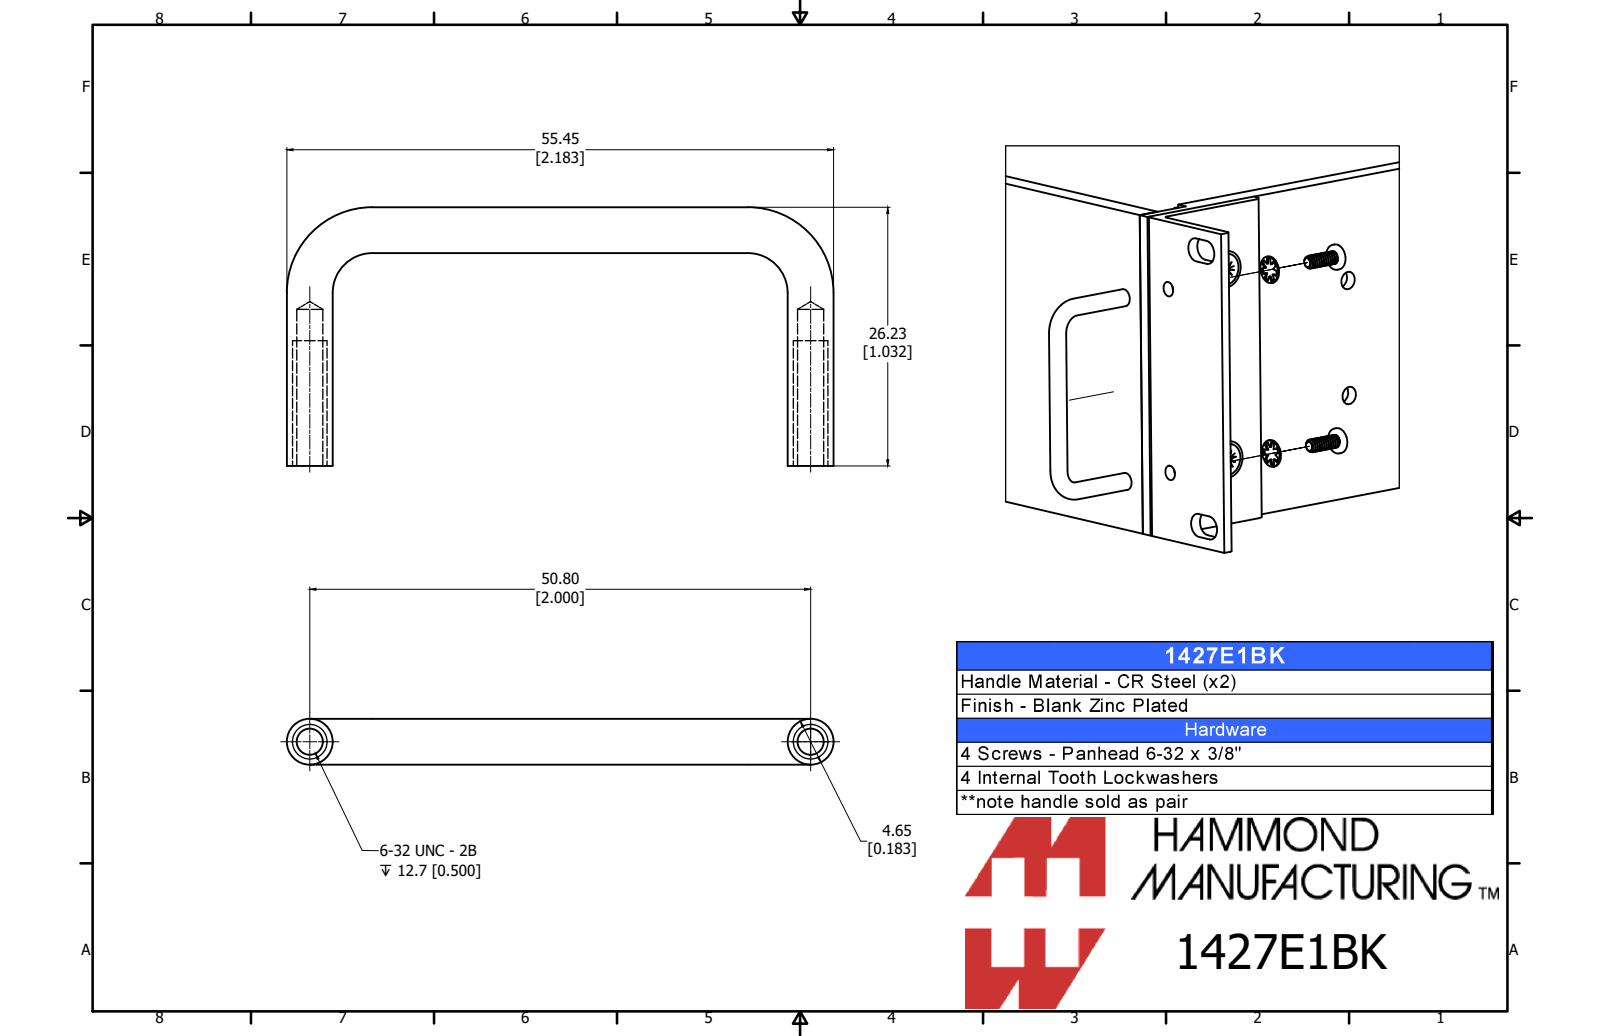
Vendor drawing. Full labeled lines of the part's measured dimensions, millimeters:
Part name (STEP PRODUCT): 1427E1BK
STEP written by: SolidWorks 2021 (AUTOMOTIVE_DESIGN)
Units: millimetres
Bodies: 1 solid, 11 faces (2 planar, 5 cylindrical, 4 other)
Overall size (bounding box): 55.4 × 26.2 × 4.6
Volume: 1 400 mm³ · Surface area: 1 661 mm²
Round holes (diameter × count): ⌀2.6 ×2
Round bosses / shafts (diameter × count): ⌀4.6 ×3
Hole centre spacings: 50.8
